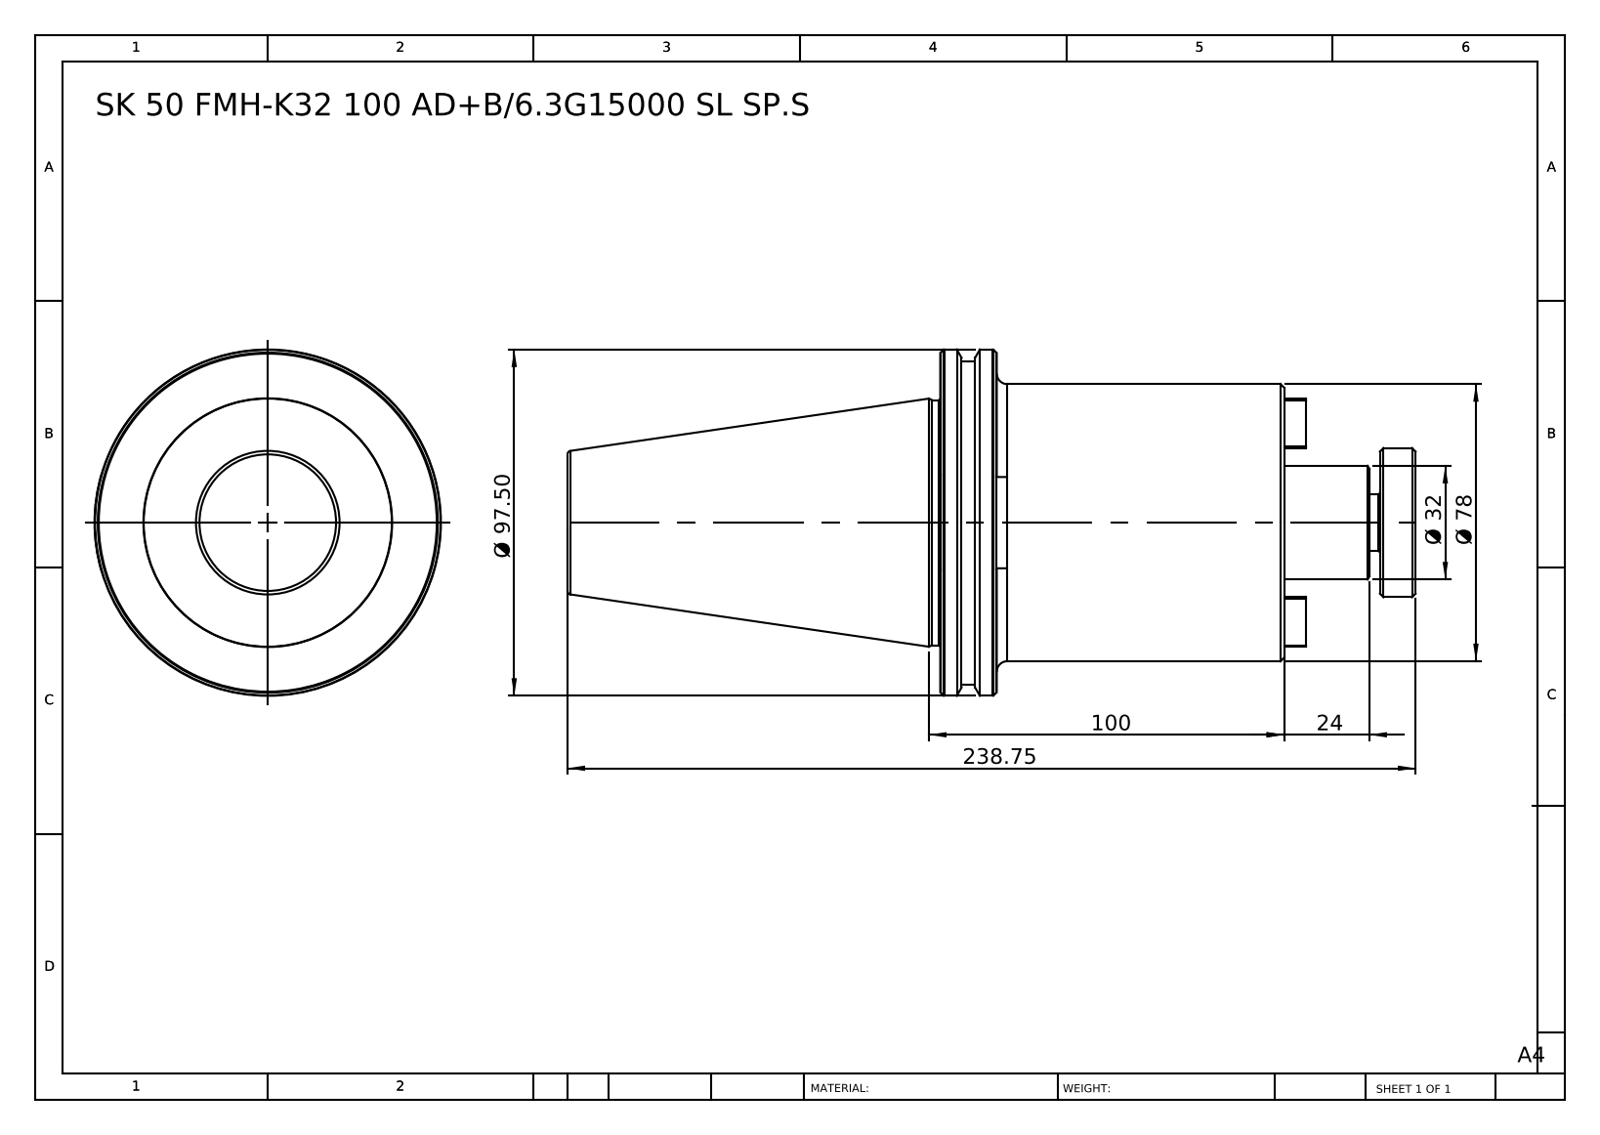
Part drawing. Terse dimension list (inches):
name: SK50 FMH32 100 AD-6.3G15000 SL SP.S
written by: SolidWorks 2014 (CONFIG_CONTROL_DESIGN)
unit: in
bodies: 1 solid, 102 faces (27 planar, 16 cylindrical, 59 other)
size: 9.4 × 3.839 × 3.839
volume: 48.61 in³; area: 97.17 in²
bosses: 1× ⌀3.839, 1× ⌀3.583, 1× ⌀3.071, 1× ⌀2.717, 1× ⌀1.654, 1× ⌀1.26, 1× ⌀0.63
face distances: 3.811, 3.185, 0.626, 1.457, 4.642, 5.268, 9.4, 7.943, 4.758, 4.132
